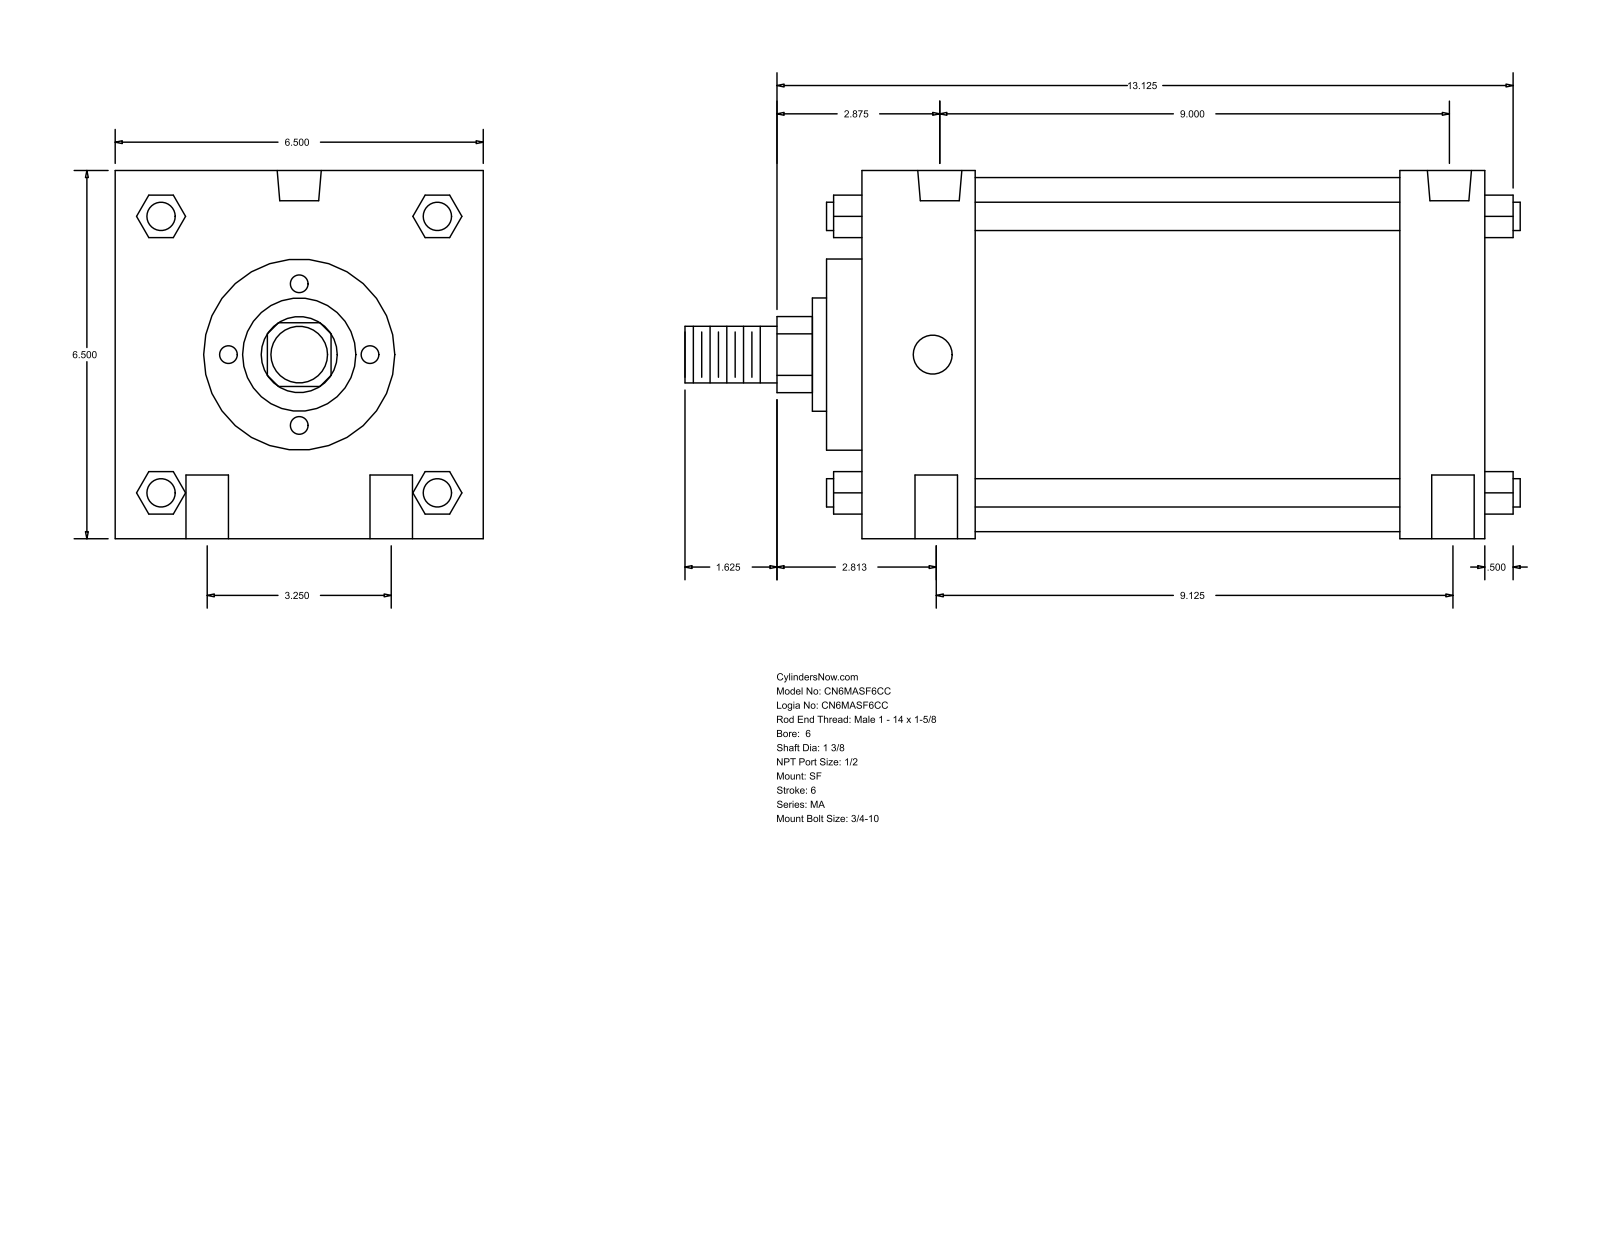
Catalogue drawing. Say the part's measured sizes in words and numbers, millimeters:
The part is named "MA_SF__0600_1.375". Its 3-D file was written by "GSSL Pune (CONFIG_CONTROL_DESIGN)". It is 0 solids with 126 faces: 95 planar, 31 cylindrical and 0 other. Overall it measures 374.65 by 165.1 by 165.1 millimeters. Round holes: 4 of diameter 19.05, 2 of diameter 17.46, 2 of diameter 19.77. Round bosses or shafts: 4 of diameter 12.7, 1 of diameter 158.75, 1 of diameter 85.72, 1 of diameter 50.8, 1 of diameter 34.92, 1 of diameter 25.4. Partial cylindrical surfaces (rounded edges, fillets, slot ends): 1 of radius 17.06. The main face-to-face distances are 165.1, 279.4, 241.3, 50.8, 38.1, 190.5, 228.6, 66.67, 15.87, 257.17. The hole center spacings are 41.3, 233.85, 82.54, 231.77, 246.03, 228.59, 228.6.
